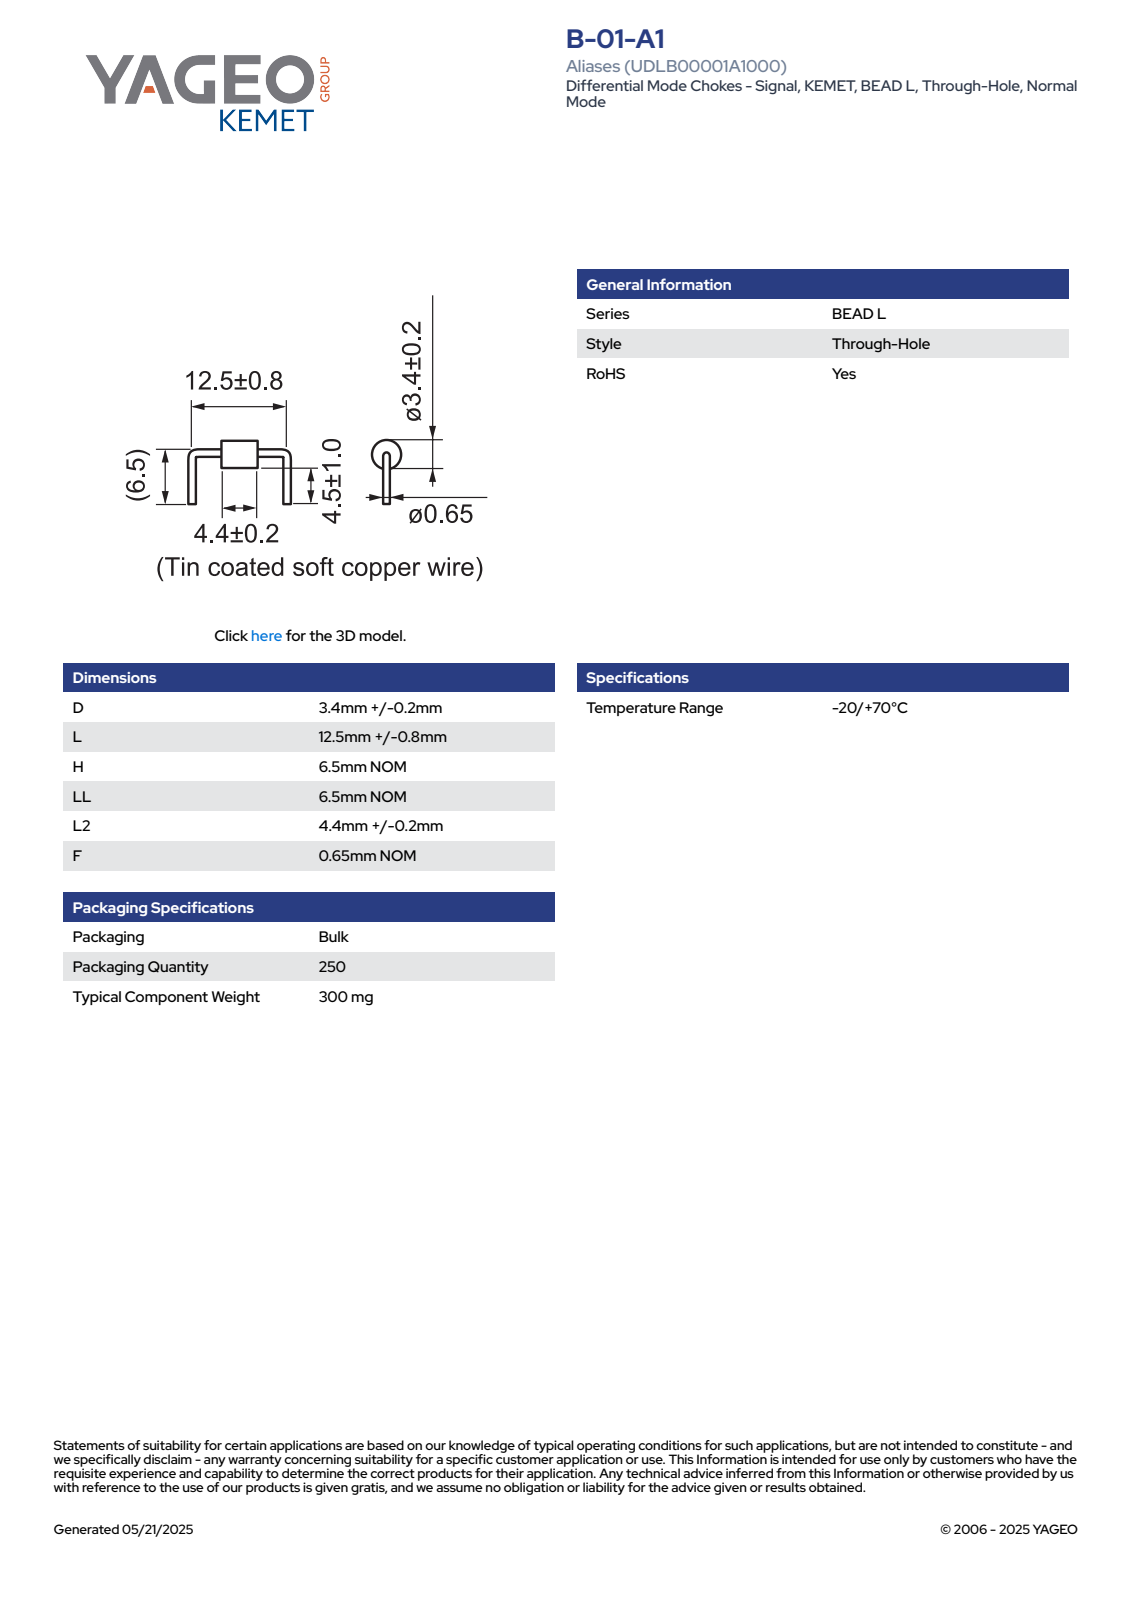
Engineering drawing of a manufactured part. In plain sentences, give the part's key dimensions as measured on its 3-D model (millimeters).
The part is named "Default". Its 3-D file was written by "SolidWorks 2014 (AUTOMOTIVE_DESIGN)". It is 1 solid with 72 faces: 26 planar, 13 cylindrical and 33 other. Overall it measures 13.3 by 8.3 by 3.61 millimeters. Its volume is 53 cubic millimeters and its surface area 117 square millimeters. Round bosses or shafts: 3 of diameter 0.65, 1 of diameter 3.6. Partial cylindrical surfaces (rounded edges, fillets, slot ends): 1 of radius 1.81. The main face-to-face distances are 4.6.
